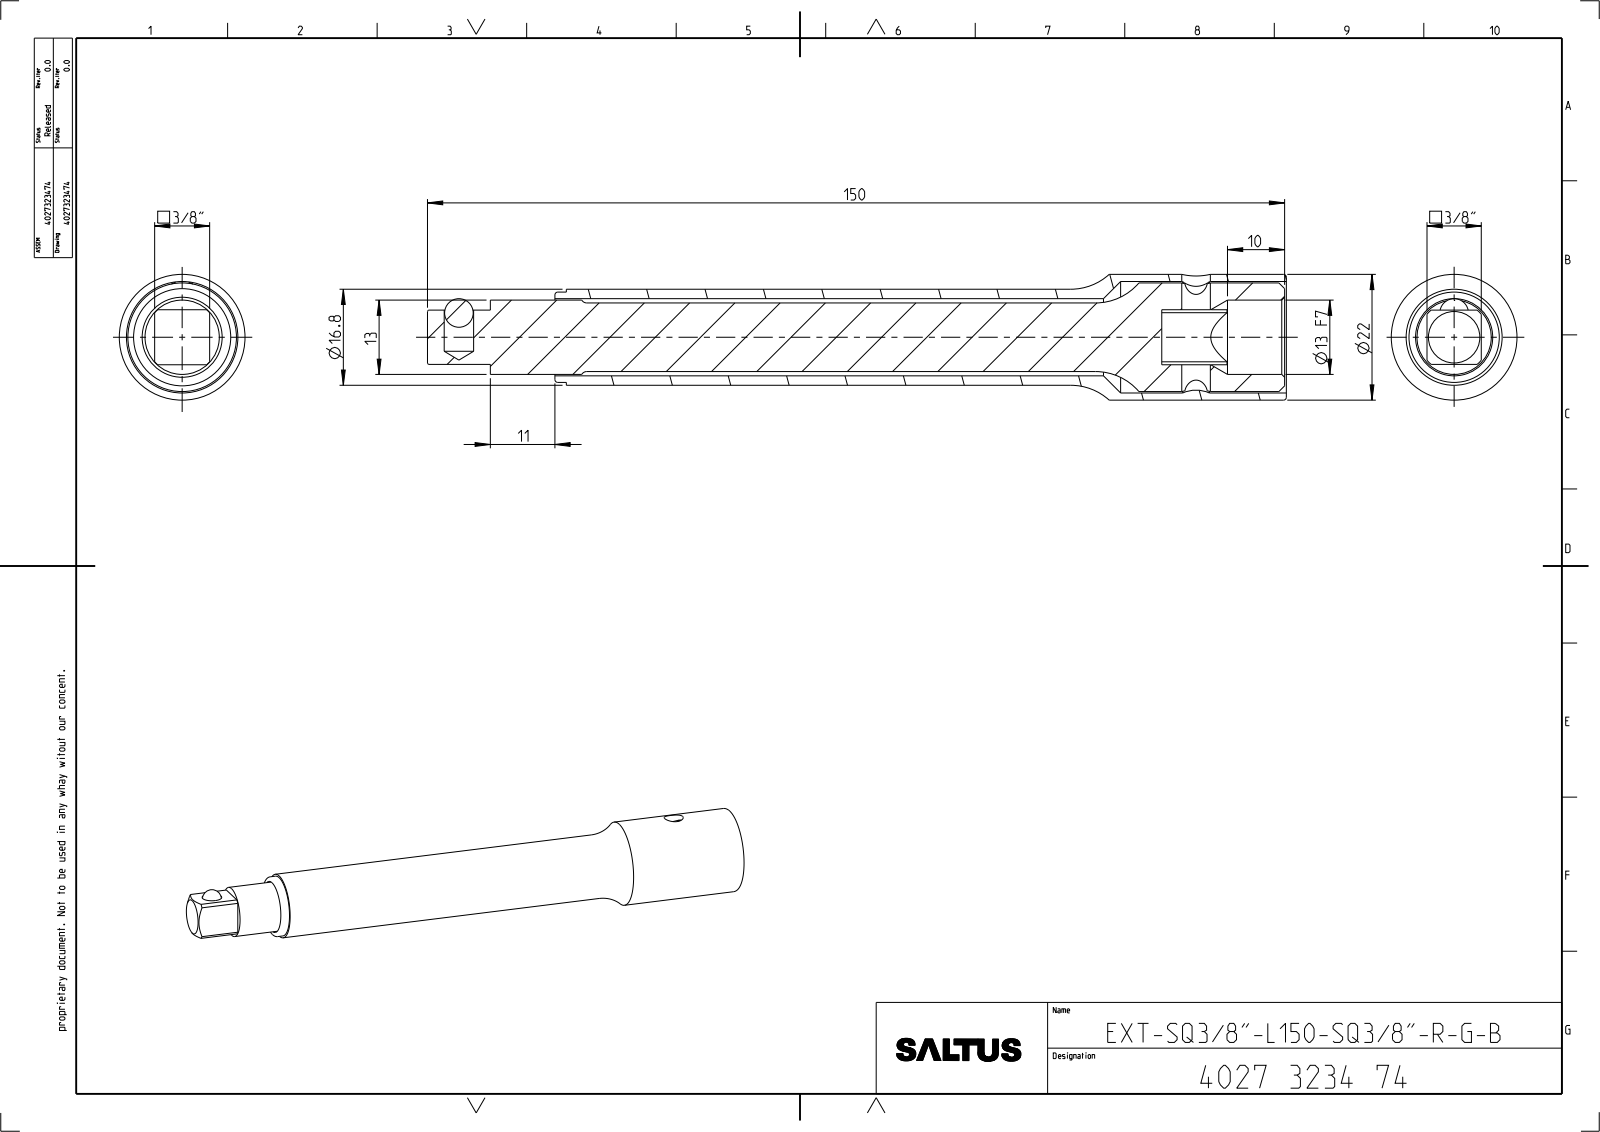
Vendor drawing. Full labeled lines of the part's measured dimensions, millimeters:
Part name (STEP PRODUCT): 4027323464; 4027299507; 4027323474_ASM
STEP written by: CREO PARAMETRIC BY PTC INC, 2022414 (CONFIG_CONTROL_DESIGN)
Units: millimetres
Bodies: 3 solids, 80 faces (15 planar, 38 cylindrical, 27 other)
Overall size (bounding box): 150.3 × 22 × 22
Volume: 29 272 mm³ · Surface area: 21 325 mm²
Round holes (diameter × count): ⌀5 ×1, ⌀5.15 ×1, ⌀13 ×1, ⌀13.5 ×1, ⌀19.5 ×1
Round bosses / shafts (diameter × count): ⌀22 ×1, ⌀19 ×1, ⌀16.8 ×1, ⌀15.8 ×1, ⌀12 ×1
Partial cylindrical surfaces — rounded edges, fillets, slot ends (radius × count): R6.22 ×1, R6.45 ×1
Main face-to-face distances: 9.56, 9.5, 9.62, 21.5, 150, 128.5, 21.8, 150.3, 139.3, 139
Hole centre spacings: 129
